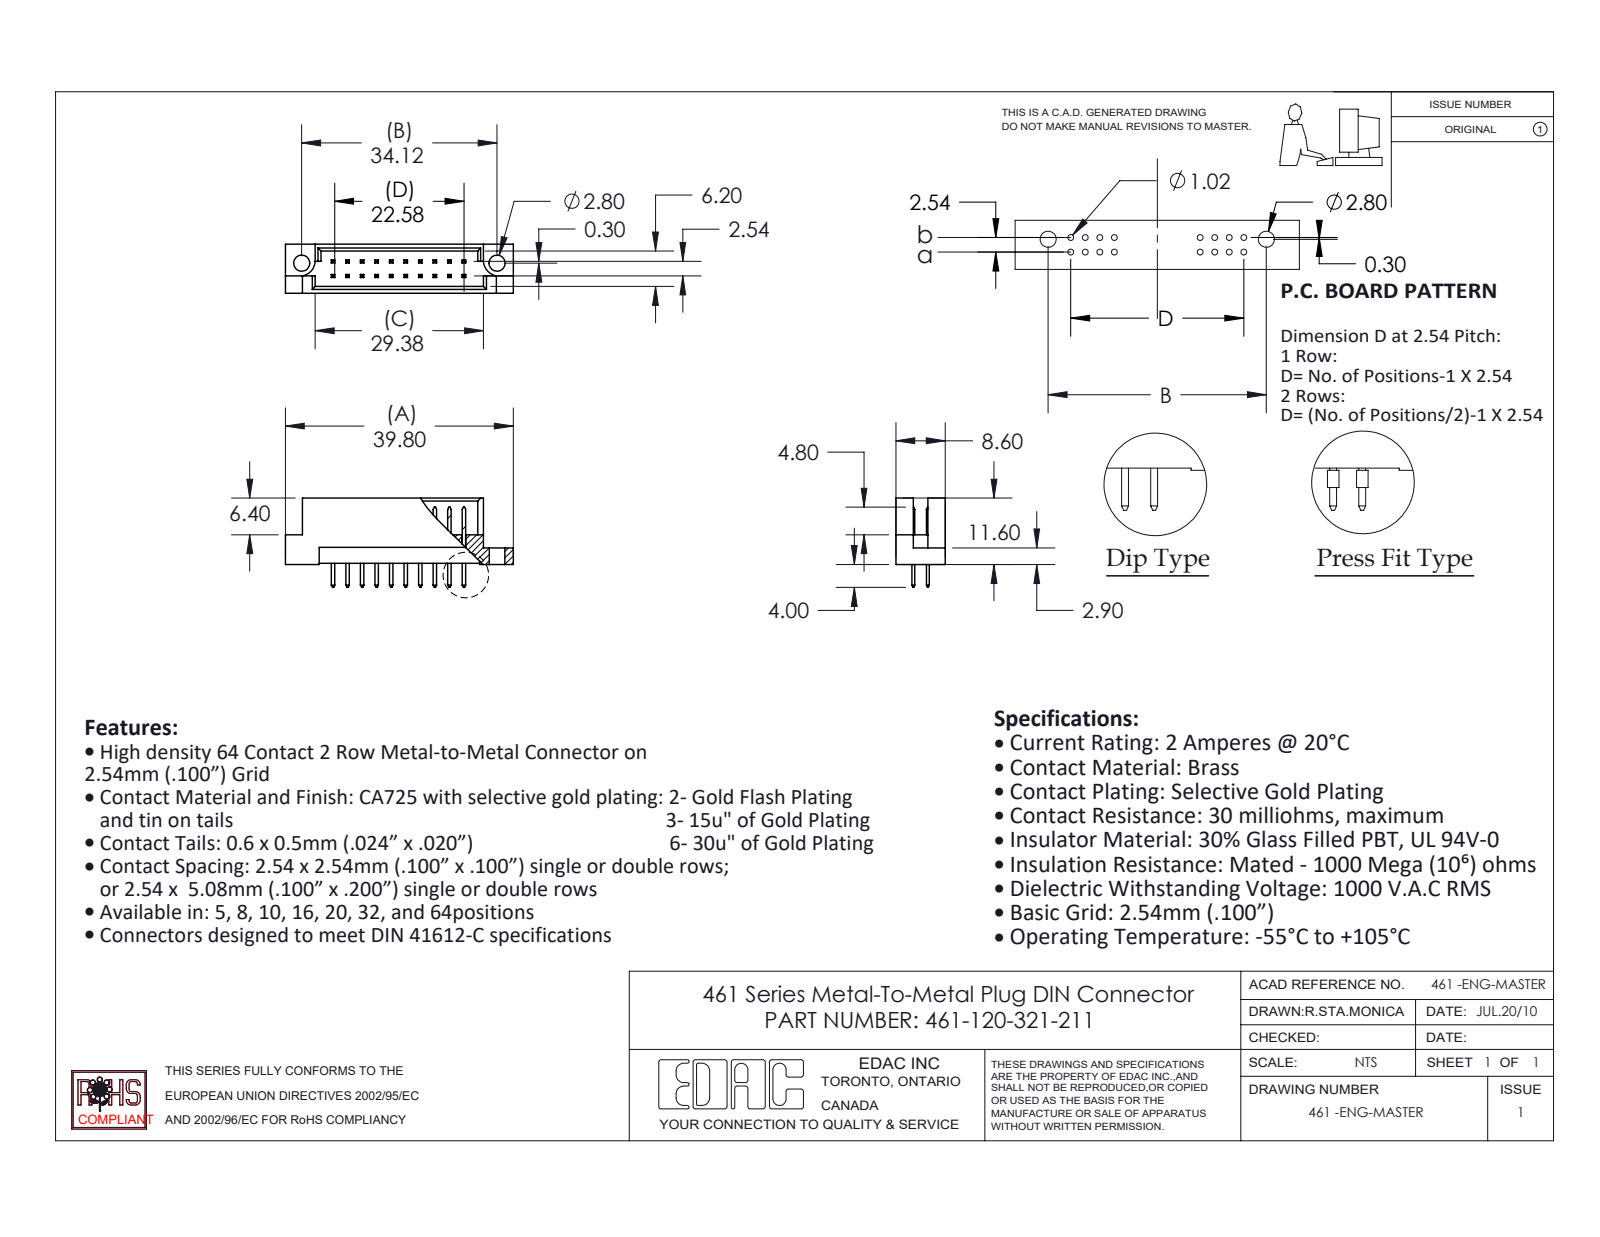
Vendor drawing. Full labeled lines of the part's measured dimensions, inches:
Part name (STEP PRODUCT): 461-120-321-211; 461 Part_20; 461-290_21
STEP written by: SolidWorks 2020 (CONFIG_CONTROL_DESIGN)
Units: inches
Bodies: 21 solids, 408 faces (402 planar, 6 cylindrical, 0 other)
Overall size (bounding box): 1.567 × 0.614 × 0.339
Volume: 0.121 in³ · Surface area: 4.566 in²
Round holes (diameter × count): ⌀0.11 ×2
Partial cylindrical surfaces — rounded edges, fillets, slot ends (radius × count): R0.11 ×2
Main face-to-face distances: 0.047, 0.291, 0.1, 0.339, 0.244, 0.129, 0.209, 0.082, 0.162, 0.109
Hole centre spacings: 1.343
